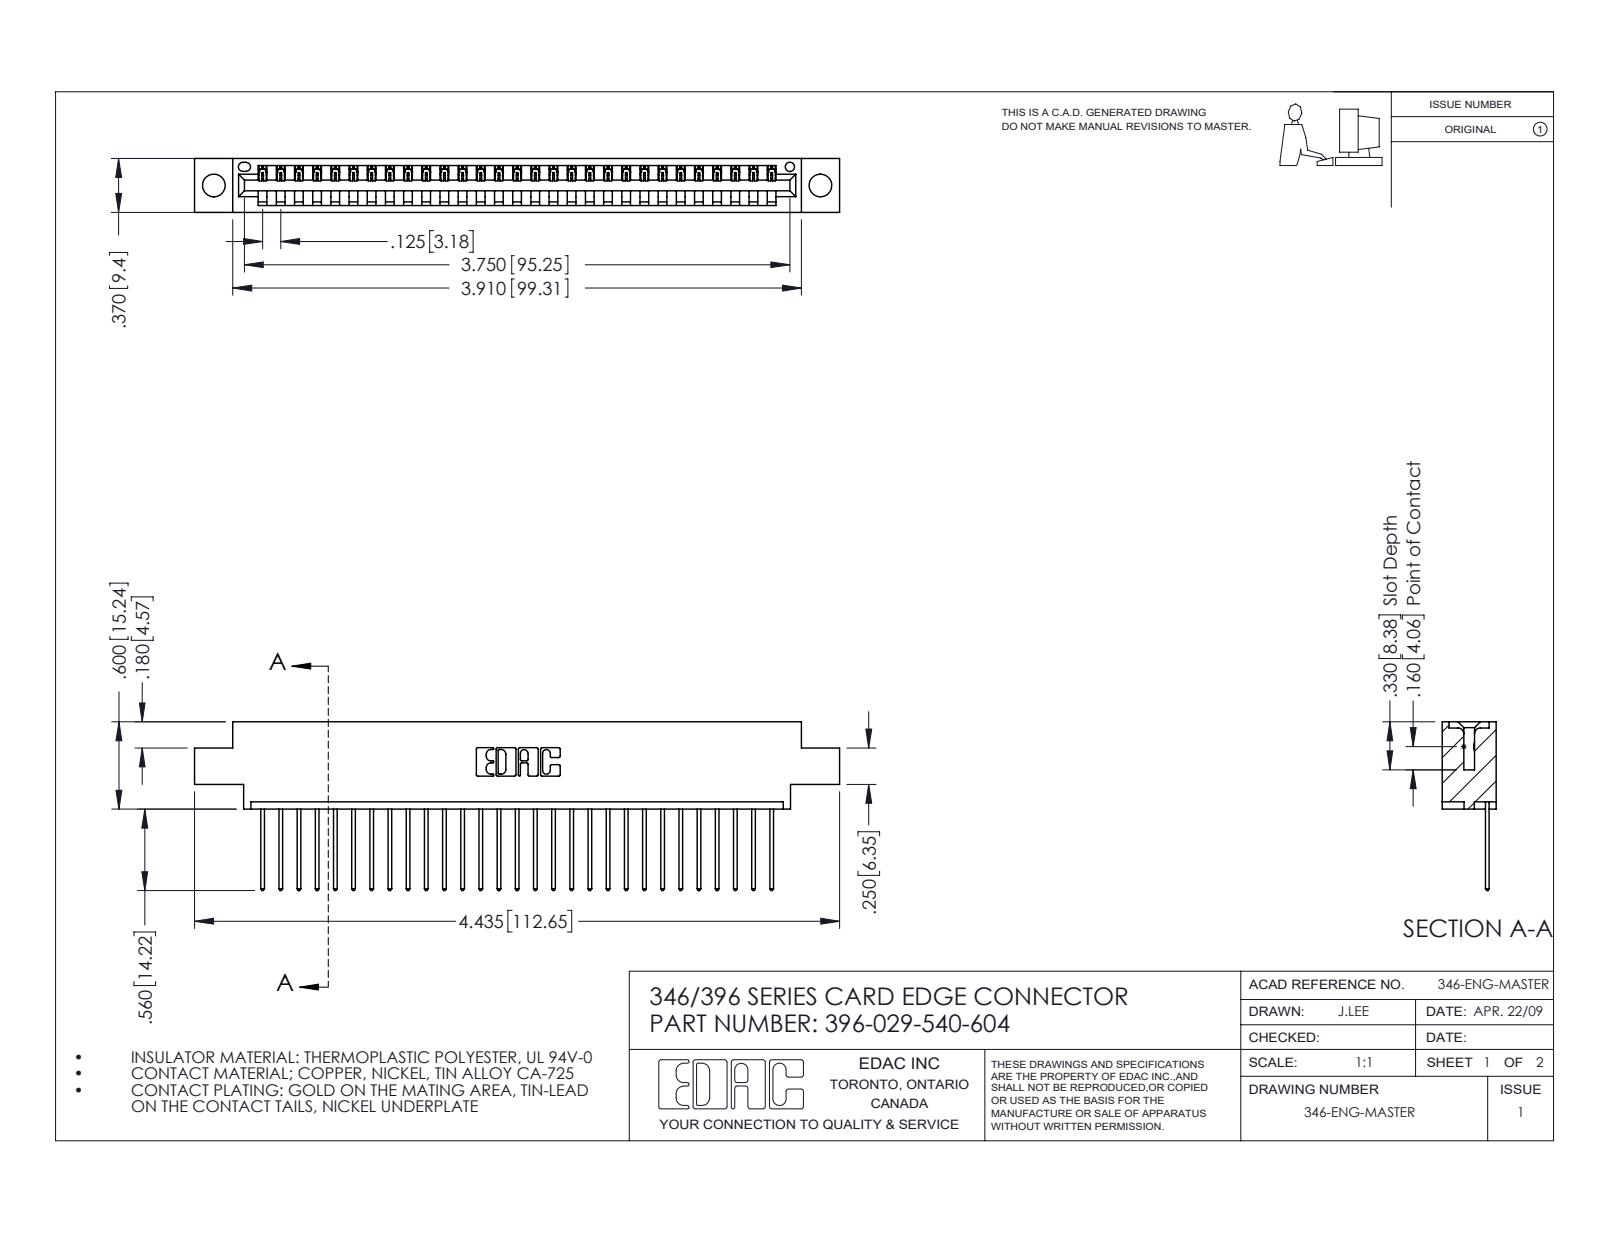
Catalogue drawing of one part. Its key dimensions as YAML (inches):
part_name: "396-029-540-604; 345-292-001_345-293-140; 346 Part_0.170 Offset - 0.156 Dia-TH"
step_written_by: "SolidWorks 2016 (CONFIG_CONTROL_DESIGN)"
units: inches
bodies: {solids: 30, faces: 1808, planar: 1240, cylindrical: 568, other: 0}
overall_size: [4.435, 1.16, 0.37]
volume: 0.64
surface_area: 20.5
round_holes:
  - {diameter: 0.156, count: 2}
  - {diameter: 0.064, count: 1}
partial_cylinders:
  - {radius: 0.006, count: 58}
  - {radius: 0.01, count: 58}
  - {radius: 0.01, count: 22}
  - {radius: 0.007, count: 6}
  - {radius: 0.031, count: 6}
  - {radius: 0.026, count: 3}
  - {radius: 0.031, count: 2}
  - {radius: 0.04, count: 2}
face_to_face_distances: [0.048, 0.322, 0.37, 0.25, 0.072, 0.298, 0.025, 0.148, 0.222, 0.1]
hole_center_spacings: [0.246, 3.962, 4.17]
